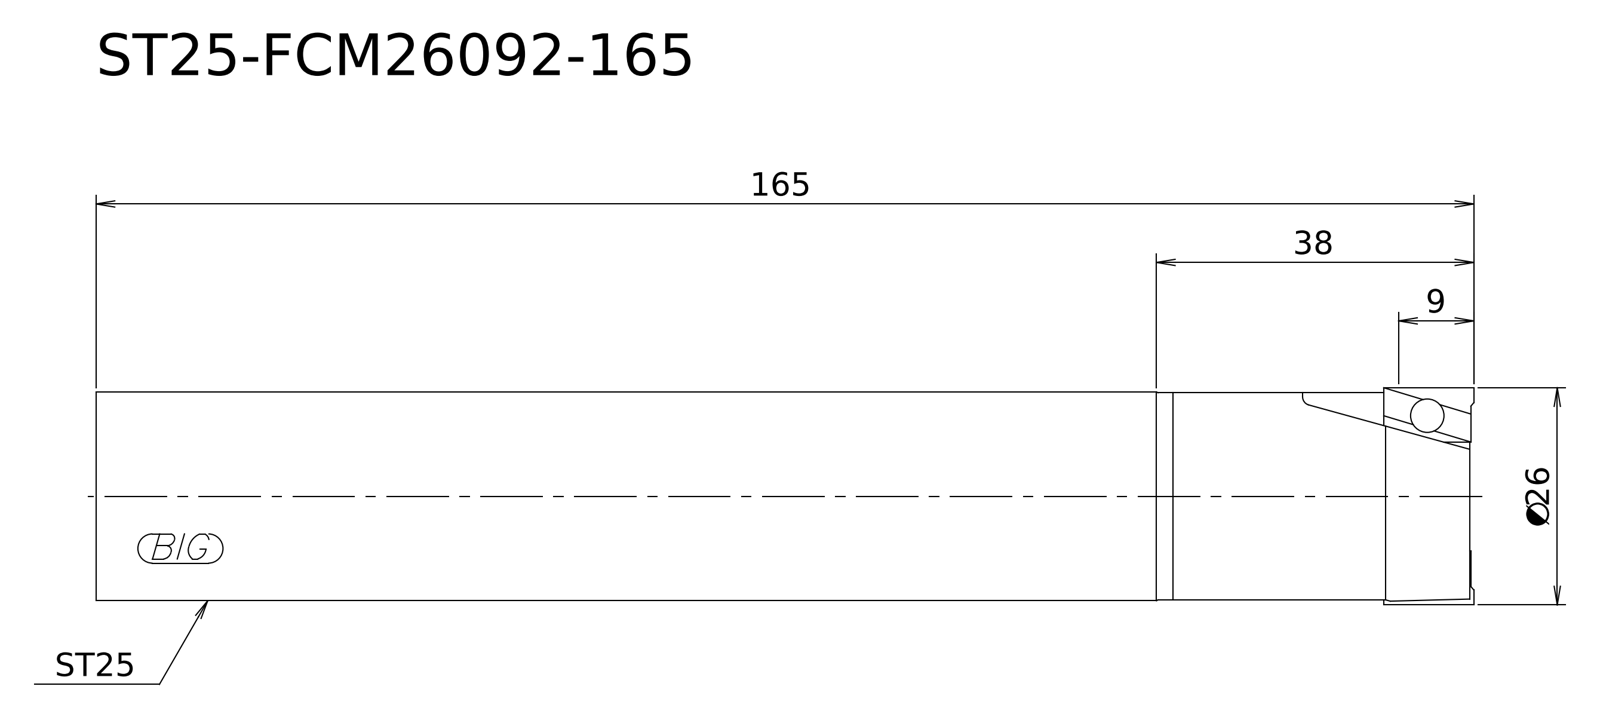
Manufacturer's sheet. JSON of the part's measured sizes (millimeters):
{"step_written_by": "Kubotek KeyCreator V8.5.1 (14335) (CONFIG_CONTROL_DESIGN)", "units": "millimeters", "bodies": {"solids": 1, "faces": 7, "planar": 3, "cylindrical": 3, "other": 1}, "overall_size": [165, 26, 26], "volume_mm3": 81214, "surface_area_mm2": 14048, "round_bosses_or_shafts": [[26, 1], [25, 1], [24.8, 1]], "face_to_face_distances": [165, 10.79, 154.21]}
